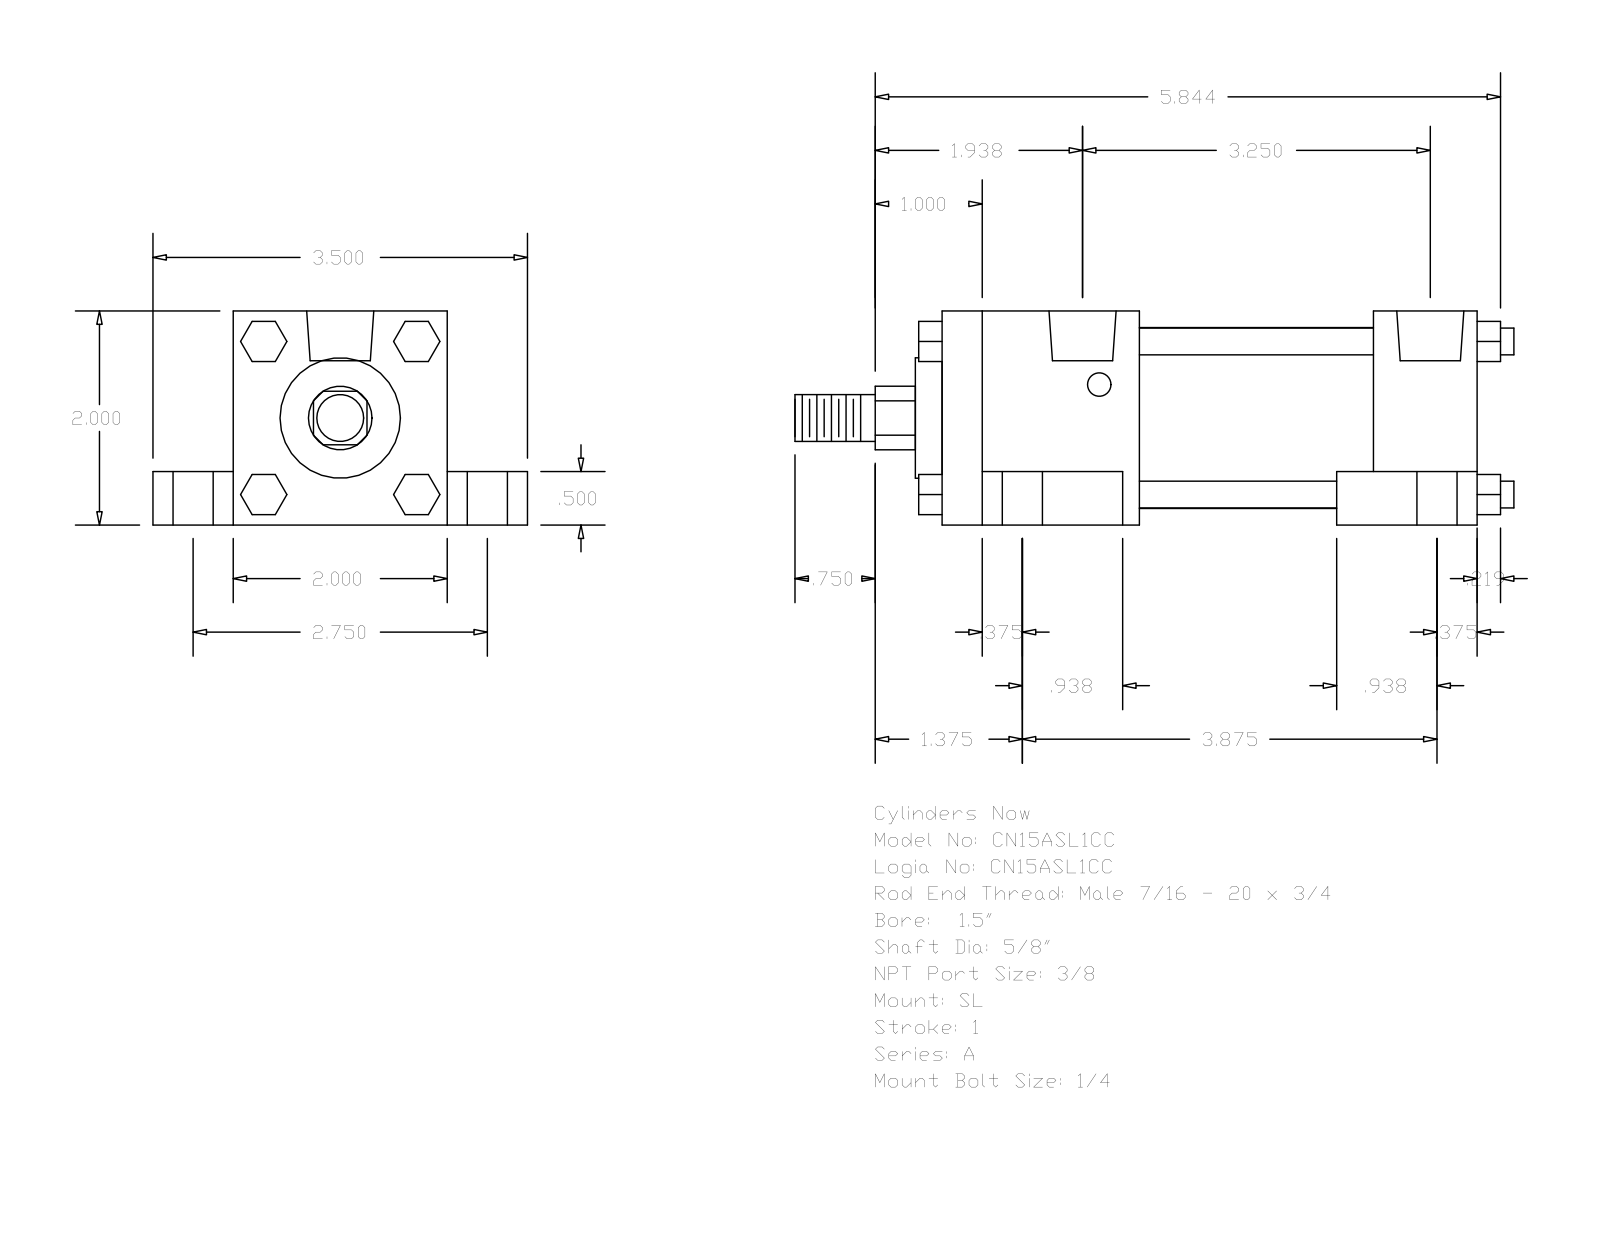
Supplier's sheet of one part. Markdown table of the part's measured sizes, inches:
| quantity | value |
| --- | --- |
| part name | A_SL__0150_0.625 |
| STEP written by | GSSL Pune (CONFIG_CONTROL_DESIGN) |
| units | inches |
| bodies | 0 solids, 148 faces (112 planar, 36 cylindrical, 0 other) |
| overall size | 6.719 × 3.5 × 2 |
| round holes (diameter × count) | 0.219 × 4, 0.375 × 4, 0.625 × 4, 0.627 × 2 |
| round bosses / shafts (diameter × count) | 0.25 × 4, 1.69 × 1, 1.125 × 1, 0.625 × 1, 0.437 × 1 |
| partial cylindrical surfaces (radius × count) | 0.297 × 1 |
| main face-to-face distances | 2, 0.75, 1.5, 0.5, 2.75, 5, 1.844, 0.375, 1.313, 4.031 |
| hole center spacings | 0.156, 1.376, 1.392, 1.485, 1.552, 2.75, 2.937, 3.094 |
